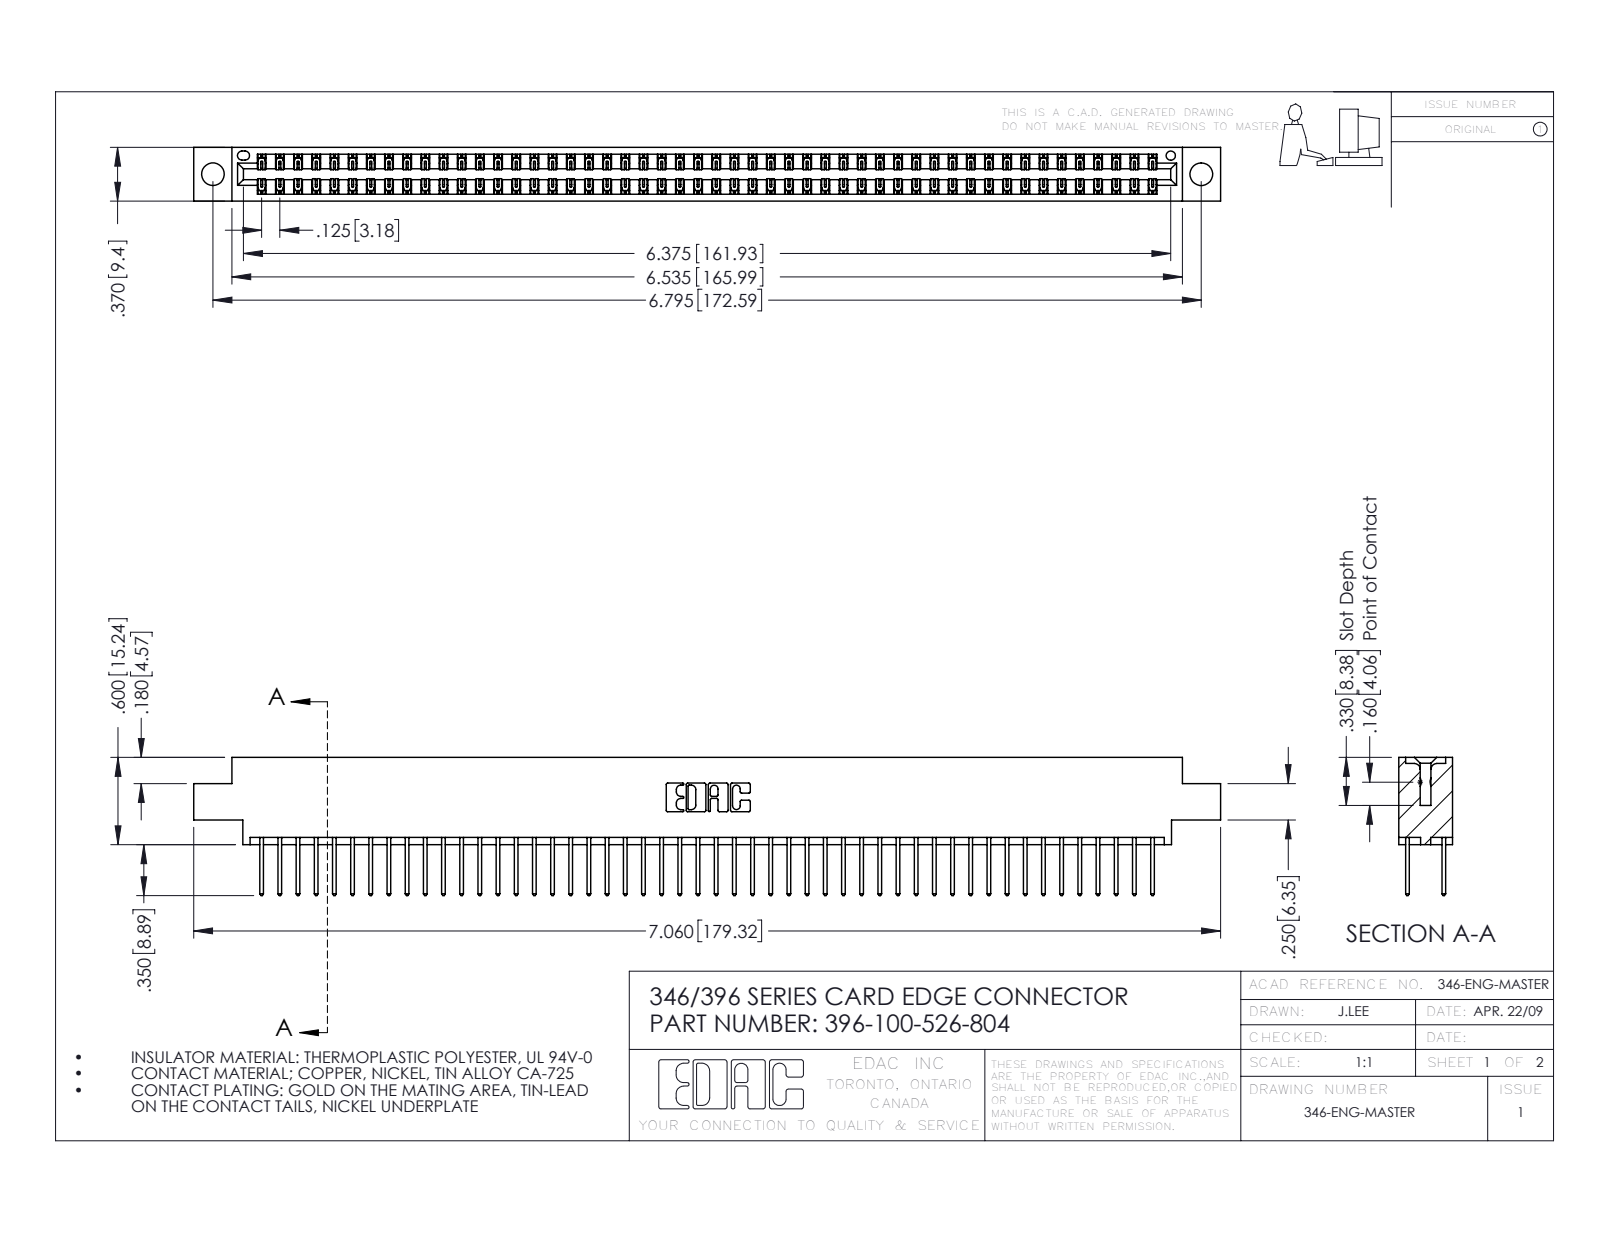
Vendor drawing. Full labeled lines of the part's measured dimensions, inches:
Part name (STEP PRODUCT): 345-292-001_345-293-126; 396-100-526-804; 346 Part_0.170 Offset - 0.156 Dia-TH
STEP written by: SolidWorks 2016 (CONFIG_CONTROL_DESIGN)
Units: inches
Bodies: 101 solids, 5326 faces (3580 planar, 1746 cylindrical, 0 other)
Overall size (bounding box): 7.06 × 0.95 × 0.37
Volume: 1.066 in³ · Surface area: 38.54 in²
Round holes (diameter × count): ⌀0.156 ×2, ⌀0.064 ×1
Partial cylindrical surfaces — rounded edges, fillets, slot ends (radius × count): R0.006 ×150, R0.01 ×100, R0.01 ×22, R0.007 ×6, R0.031 ×6, R0.026 ×3, R0.014 ×2, R0.022 ×2
Main face-to-face distances: 0.048, 0.322, 0.25, 0.37, 0.072, 0.298, 0.025, 0.275, 0.148, 0.222
Hole centre spacings: 0.246, 6.586, 6.795
